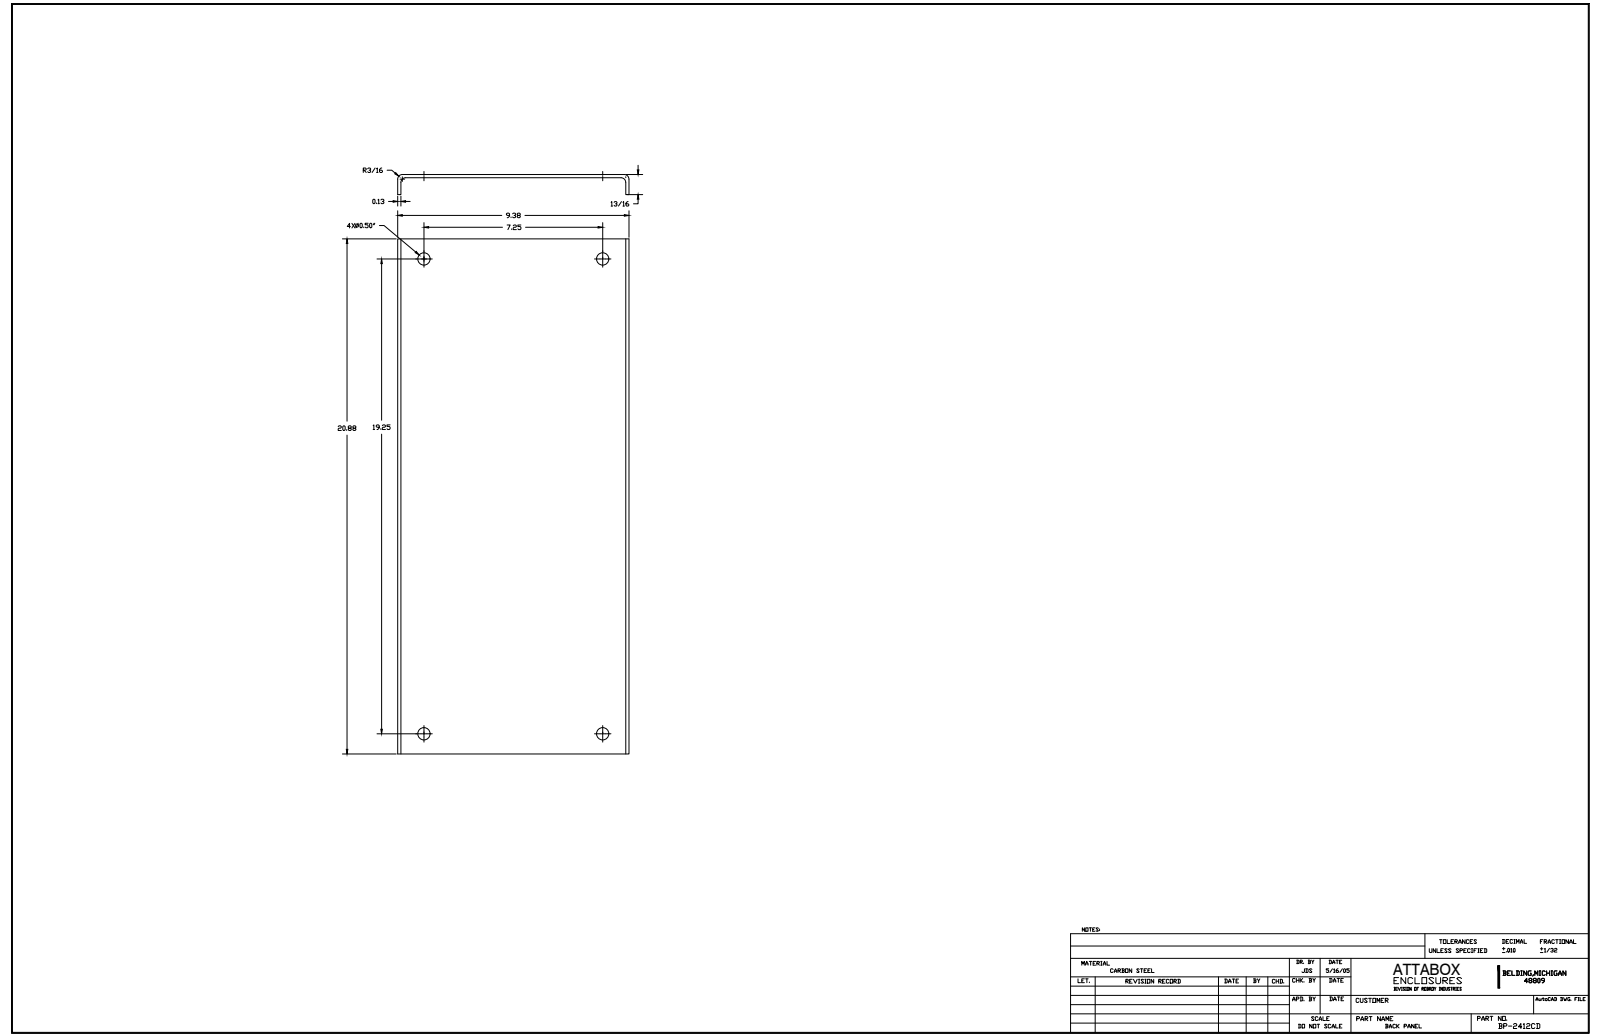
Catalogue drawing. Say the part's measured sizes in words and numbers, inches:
The part is named "BP2412CD". Its 3-D file was written by "SolidWorks 2018 (AUTOMOTIVE_DESIGN)". It is 1 solid with 18 faces: 10 planar, 8 cylindrical and 0 other. Overall it measures 20.875 by 9.375 by 0.5 inches. Its volume is 27.07 cubic inches and its surface area 425.1 square inches. Round holes: 4 of diameter 0.5. Partial cylindrical surfaces (rounded edges, fillets, slot ends): 2 of radius 0.063, 2 of radius 0.188. The main face-to-face distances are 0.13, 9.245, 9.375, 9.115, 0.37, 0.5, 20.875. The hole center spacings are 19.25, 20.57, 7.25, 7.25.
